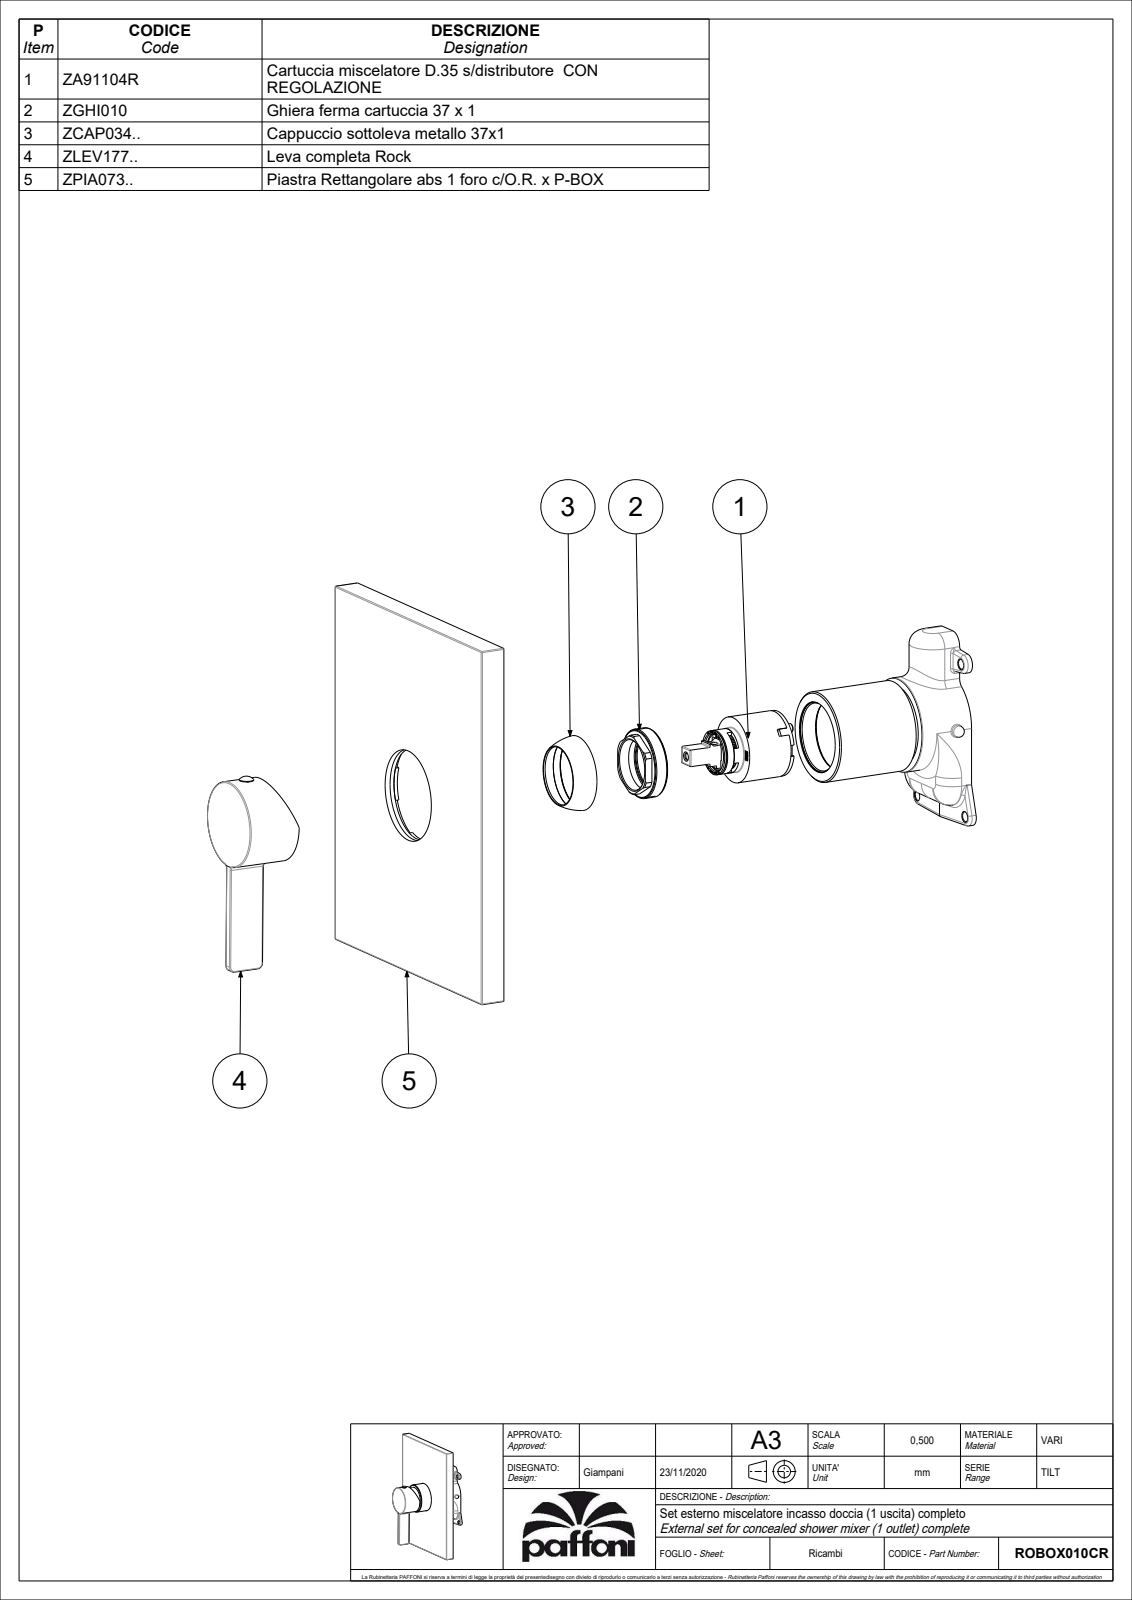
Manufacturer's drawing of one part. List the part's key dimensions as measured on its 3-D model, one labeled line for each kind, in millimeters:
Part name (STEP PRODUCT): ROBOX010CR
STEP written by: CREO PARAMETRIC BY PTC INC, 2020044 (CONFIG_CONTROL_DESIGN)
Units: millimetres
Bodies: 2 solids, 168 faces (51 planar, 57 cylindrical, 60 other)
Overall size (bounding box): 192 × 154 × 65.6
Volume: 434 582 mm³ · Surface area: 90 567 mm²
Round holes (diameter × count): ⌀3 ×1, ⌀4.2 ×1, ⌀5.5 ×1, ⌀30.6 ×1, ⌀36 ×1, ⌀37.5 ×1
Round bosses / shafts (diameter × count): ⌀48.1 ×1, ⌀45.5 ×1, ⌀7.6 ×1
Partial cylindrical surfaces — rounded edges, fillets, slot ends (radius × count): R0.5 ×17, R0.3 ×2, R1.5 ×2, R2 ×2, R3 ×2, R3.5 ×1
Main face-to-face distances: 13.5, 154, 74.75, 79.25, 192, 4.5, 61.6, 48.1, 20, 33.5
